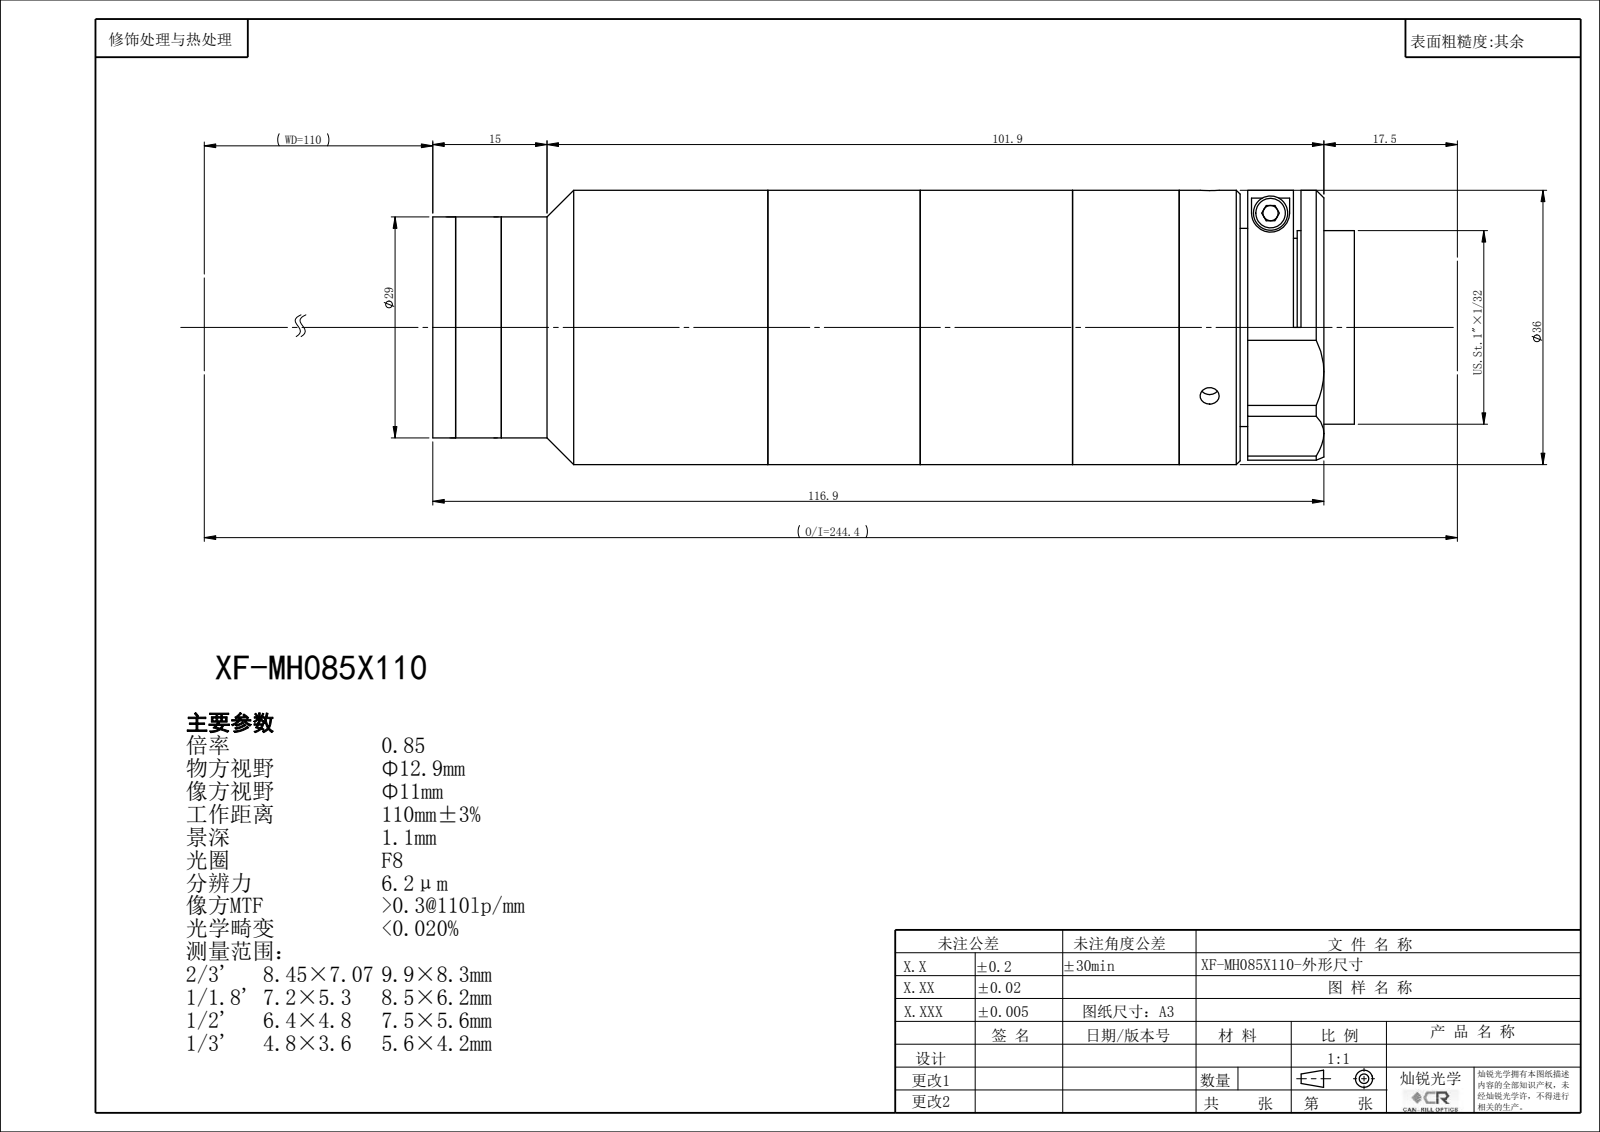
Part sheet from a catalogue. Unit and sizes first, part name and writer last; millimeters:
Units: millimetres
Overall size (bounding box): 120.93 × 36 × 36
Round holes (diameter × count): ⌀2.5 ×3, ⌀18 ×1, ⌀22.4 ×1, ⌀24 ×1, ⌀24.9 ×1, ⌀26.4 ×1
Round bosses / shafts (diameter × count): ⌀36 ×1, ⌀34 ×1, ⌀29 ×1, ⌀25.4 ×1
Main face-to-face distances: 18.93, 1.5, 17.43, 14, 31.43, 32.93, 40, 54, 71.43, 72.93
Bodies: 0 solids, 133 faces (67 planar, 44 cylindrical, 22 other)
Part name (STEP PRODUCT): XF-MH085X110
STEP written by: SolidWorks 2022 (CONFIG_CONTROL_DESIGN)
